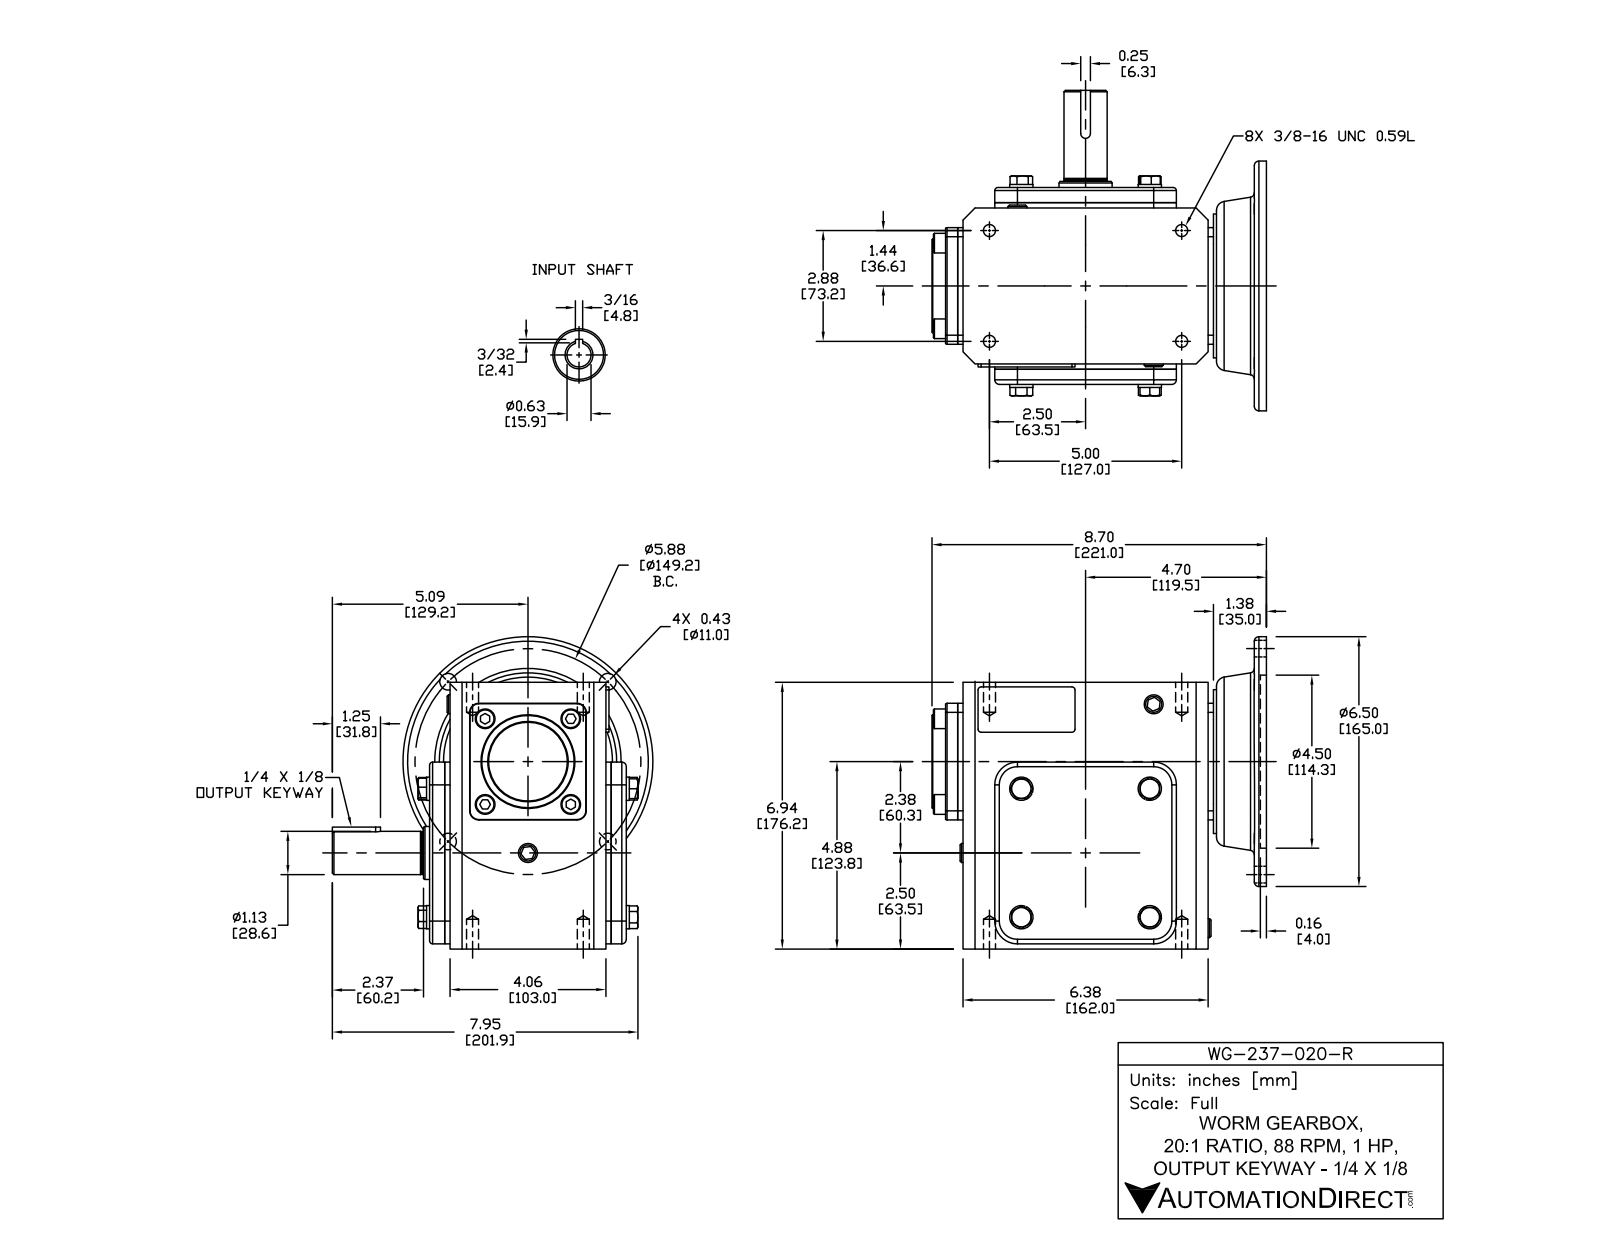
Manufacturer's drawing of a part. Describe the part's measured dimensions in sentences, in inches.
The part is named "WG-237-020-R". Its 3-D file was written by "SolidWorks 2015 (CONFIG_CONTROL_DESIGN)". It is 37 solids with 537 faces: 294 planar, 153 cylindrical and 90 other. Overall it measures 8.701 by 8.335 by 8.123 inches. Its volume is 222.4 cubic inches and its surface area 508.3 square inches. Round holes: 4 of diameter 0.313, 4 of diameter 0.406, 1 of diameter 0.591, 1 of diameter 0.625, 1 of diameter 1.378, 1 of diameter 1.457, 1 of diameter 1.772, 1 of diameter 3.819, 1 of diameter 4.5. Round bosses or shafts: 4 of diameter 0.606, 4 of diameter 0.512, 1 of diameter 6.496, 1 of diameter 3.74, 1 of diameter 2.441, 1 of diameter 2.047, 1 of diameter 1.181, 1 of diameter 1.142. Partial cylindrical surfaces (rounded edges, fillets, slot ends): 12 of radius 0.079, 6 of radius 0.236, 4 of radius 0.118, 4 of radius 0.591, 2 of radius 0.02, 2 of radius 0.039, 1 of radius 0.125. The main face-to-face distances are 0.138, 4.724, 0.394, 4.331, 0.531, 4.587, 4.193, 6.516, 6.937, 0.315. The hole center spacings are 2.937, 2.098, 2.88, 4.154, 4.154, 4.913, 5, 5.77.
